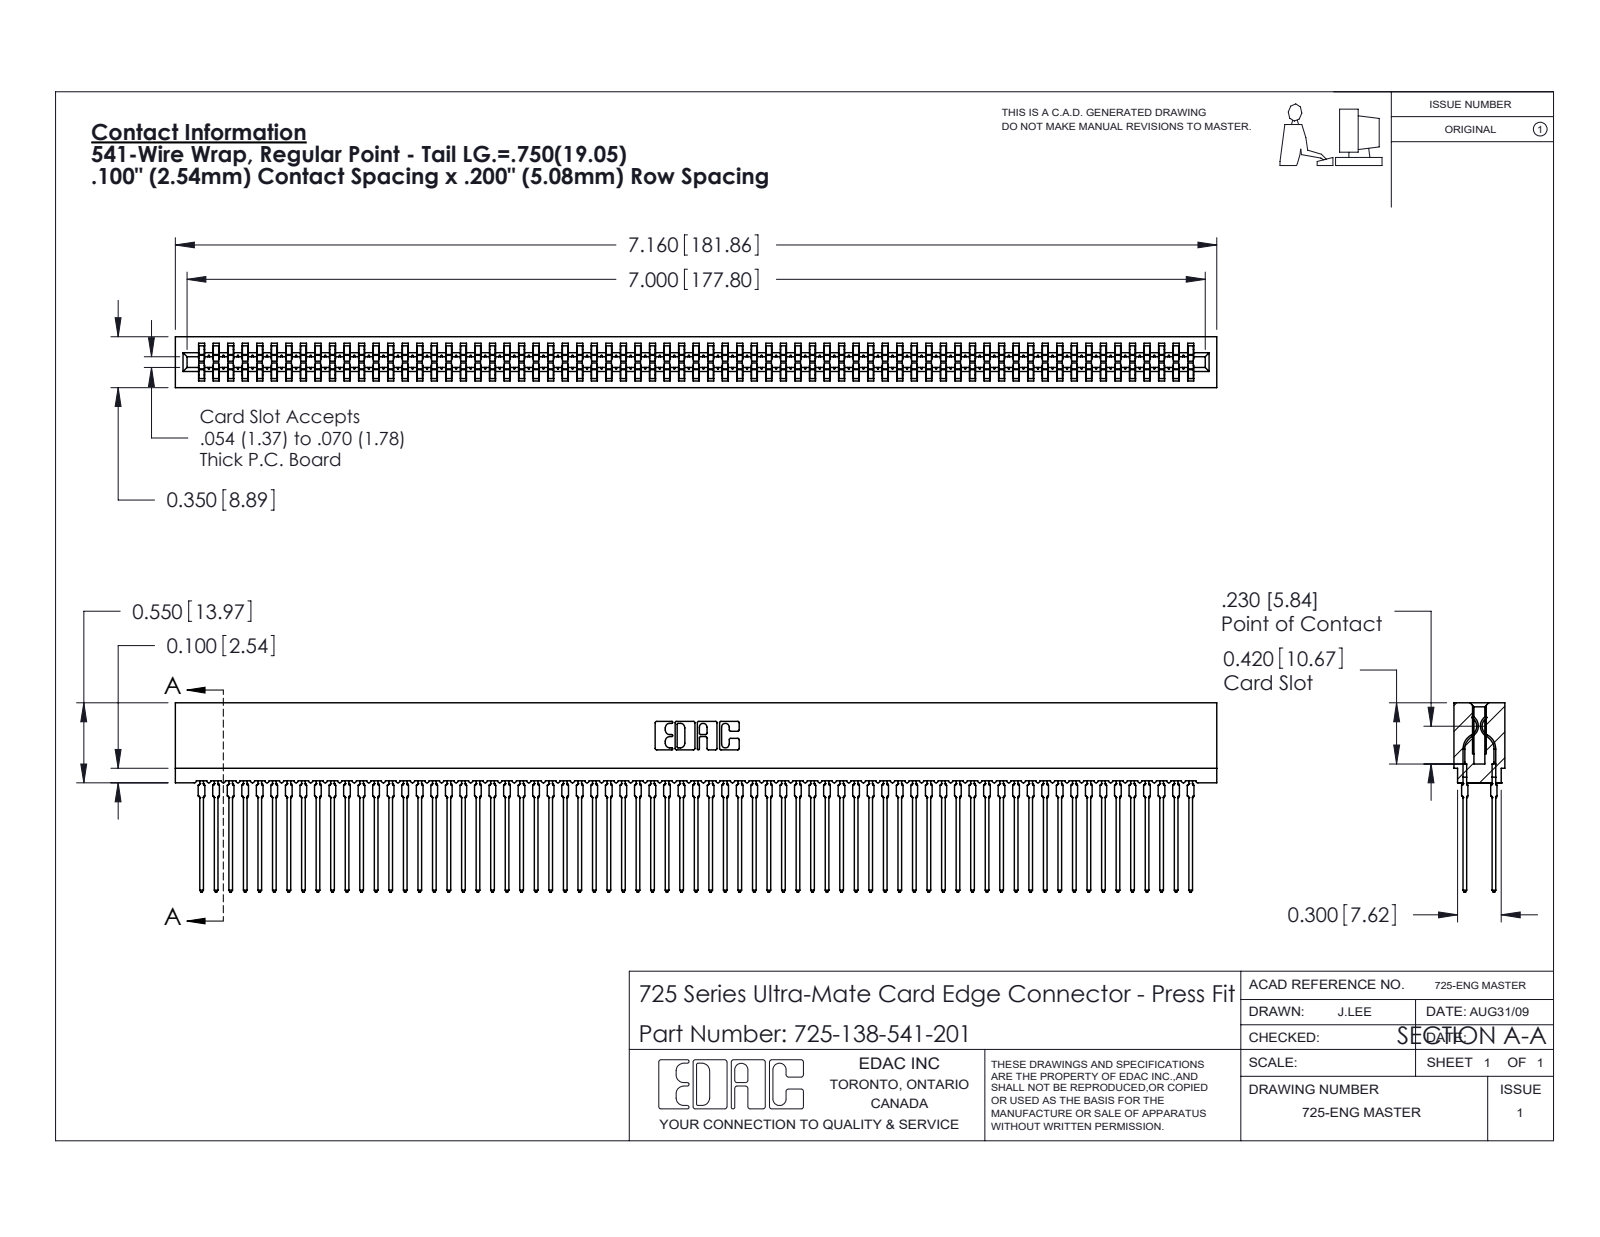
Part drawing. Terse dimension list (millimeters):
name: 725 Part_Insulator Option - 01; 745-292-001_541; 725-138-541-201
written by: SolidWorks 2020 (CONFIG_CONTROL_DESIGN)
unit: mm
bodies: 139 solids, 12446 faces (6403 planar, 2455 cylindrical, 3588 other)
size: 181.9 × 33 × 8.9
volume: 15 000 mm³; area: 34 910 mm²
rounds: 276× R0.5, 138× R0.4, 22× R0.3, 8× R0.1, 8× R0.3, 6× R0.2, 6× R0.8, 3× R0.7
face distances: 1.6, 7.3, 5.1, 2.2, 6.7, 0.6, 8.9, 5.4, 3.5, 1.9
